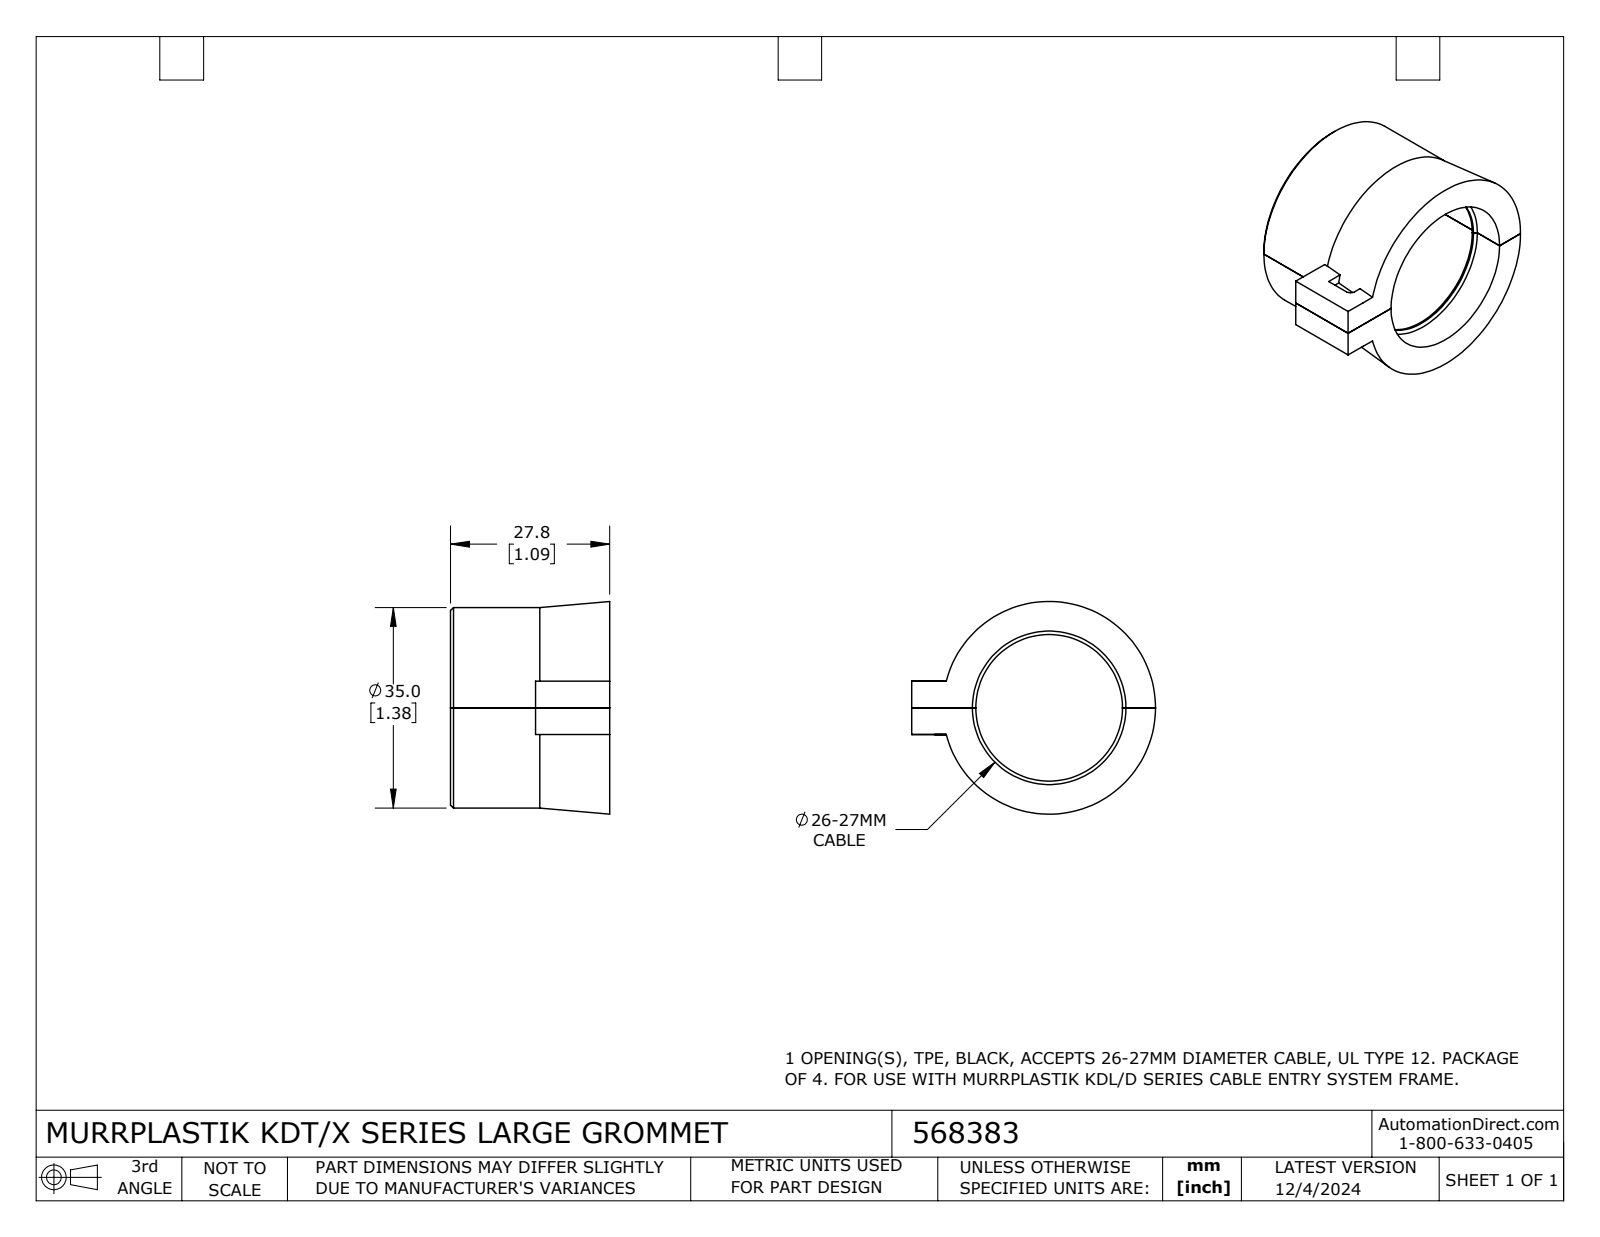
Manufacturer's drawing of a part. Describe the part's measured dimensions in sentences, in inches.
The part is named "568383". Its 3-D file was written by "SolidWorks 2024 (AUTOMOTIVE_DESIGN)". It is 2 solids with 46 faces: 22 planar, 14 cylindrical and 10 other. Overall it measures 1.676 by 1.462 by 1.094 inches. Its volume is 0.764 cubic inches and its surface area 11.39 square inches. Round holes: 1 of diameter 1.008, 1 of diameter 1.055. Round bosses or shafts: 1 of diameter 1.378. Partial cylindrical surfaces (rounded edges, fillets, slot ends): 4 of radius 0.02, 1 of radius 0.039. The main face-to-face distances are 1.094, 0.183, 0.366, 0.51, 0.585, 0.061, 0.305, 0.122, 0.157, 0.243.
